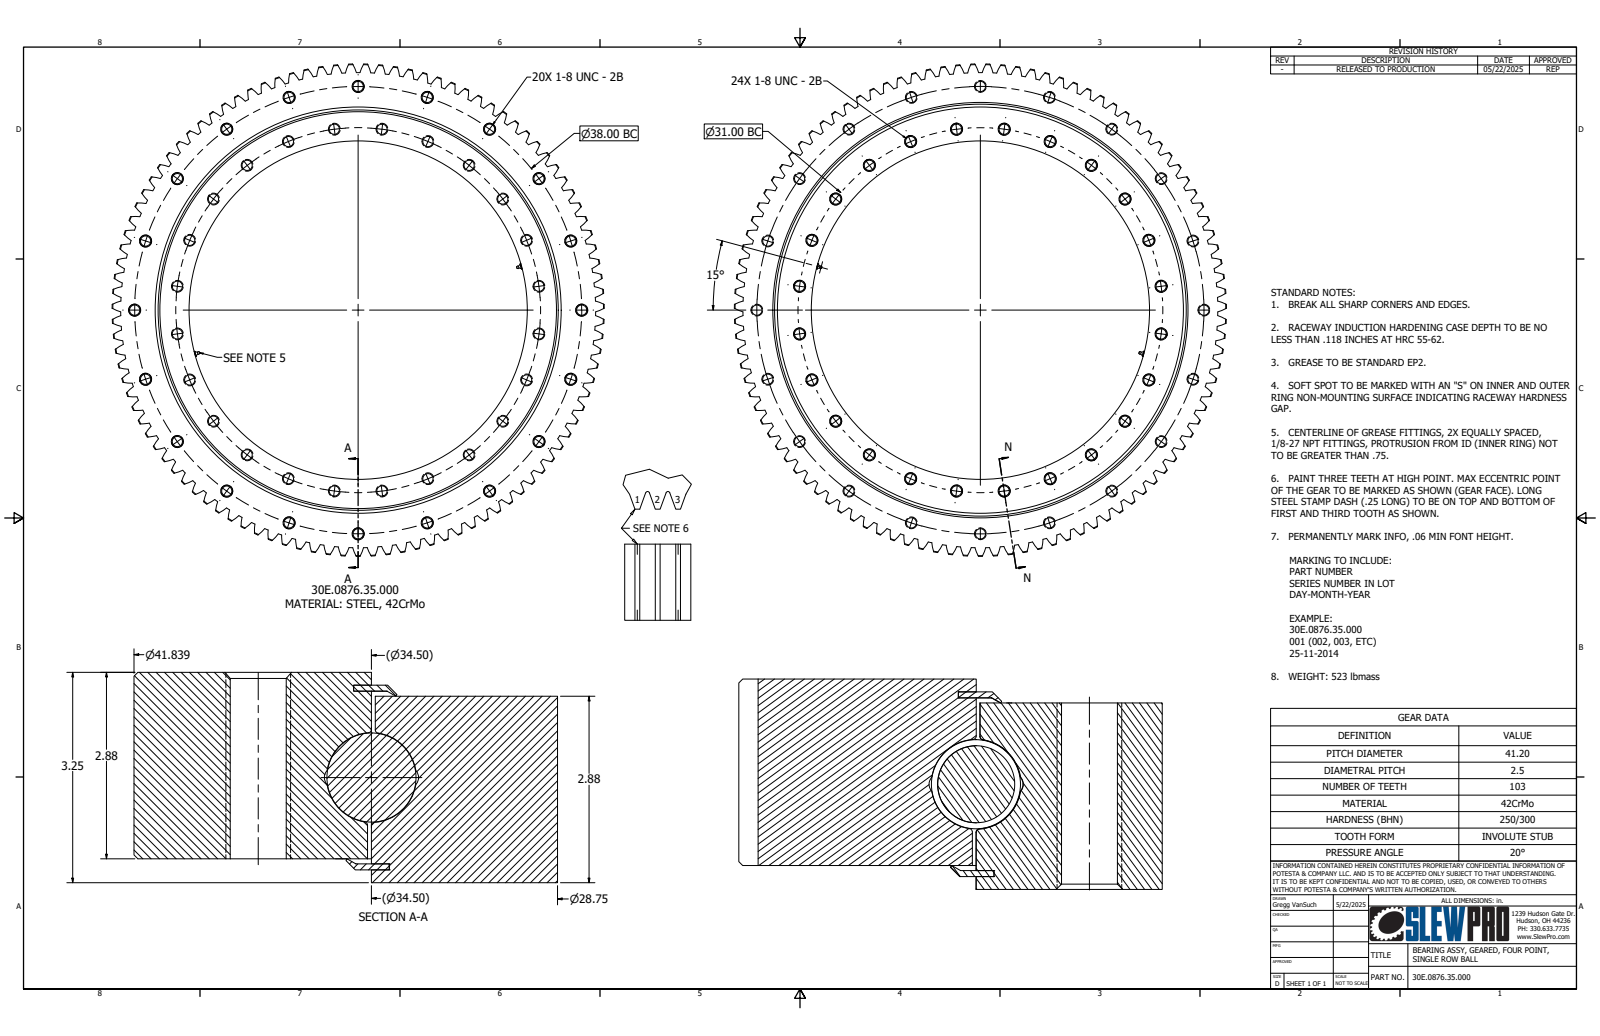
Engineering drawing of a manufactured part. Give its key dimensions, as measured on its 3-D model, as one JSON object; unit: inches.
{"part_name": "30E.0876.35.000; Spur Gears1; 1_8 NPT Fitting", "step_written_by": "Autodesk Inventor 2026 (AUTOMOTIVE_DESIGN)", "units": "inches", "bodies": {"solids": 8, "faces": 905, "planar": 36, "cylindrical": 476, "other": 393}, "overall_size": [41.837, 41.833, 3.25], "volume_in3": 1844, "surface_area_in2": 4231, "round_holes": [[0.865, 44], [0.1, 2], [1.505, 1], [28.75, 1], [33.95, 1], [34.62, 1], [35.051, 1]], "round_bosses_or_shafts": [[35.05, 1], [34.5, 1], [34.38, 1], [33.949, 1], [1.503, 1]], "partial_cylinders_radius": [[4.246, 206], [20.18, 1], [20.919, 1]], "face_to_face_distances": [2.88, 0.37, 3.25, 2.51, 2.681, 0.079, 2.76, 2.589, 0.171, 0.093], "hole_center_spacings": [15.5, 8.023, 21.92, 28.64, 29.944, 30.735, 26.847, 4.046]}
